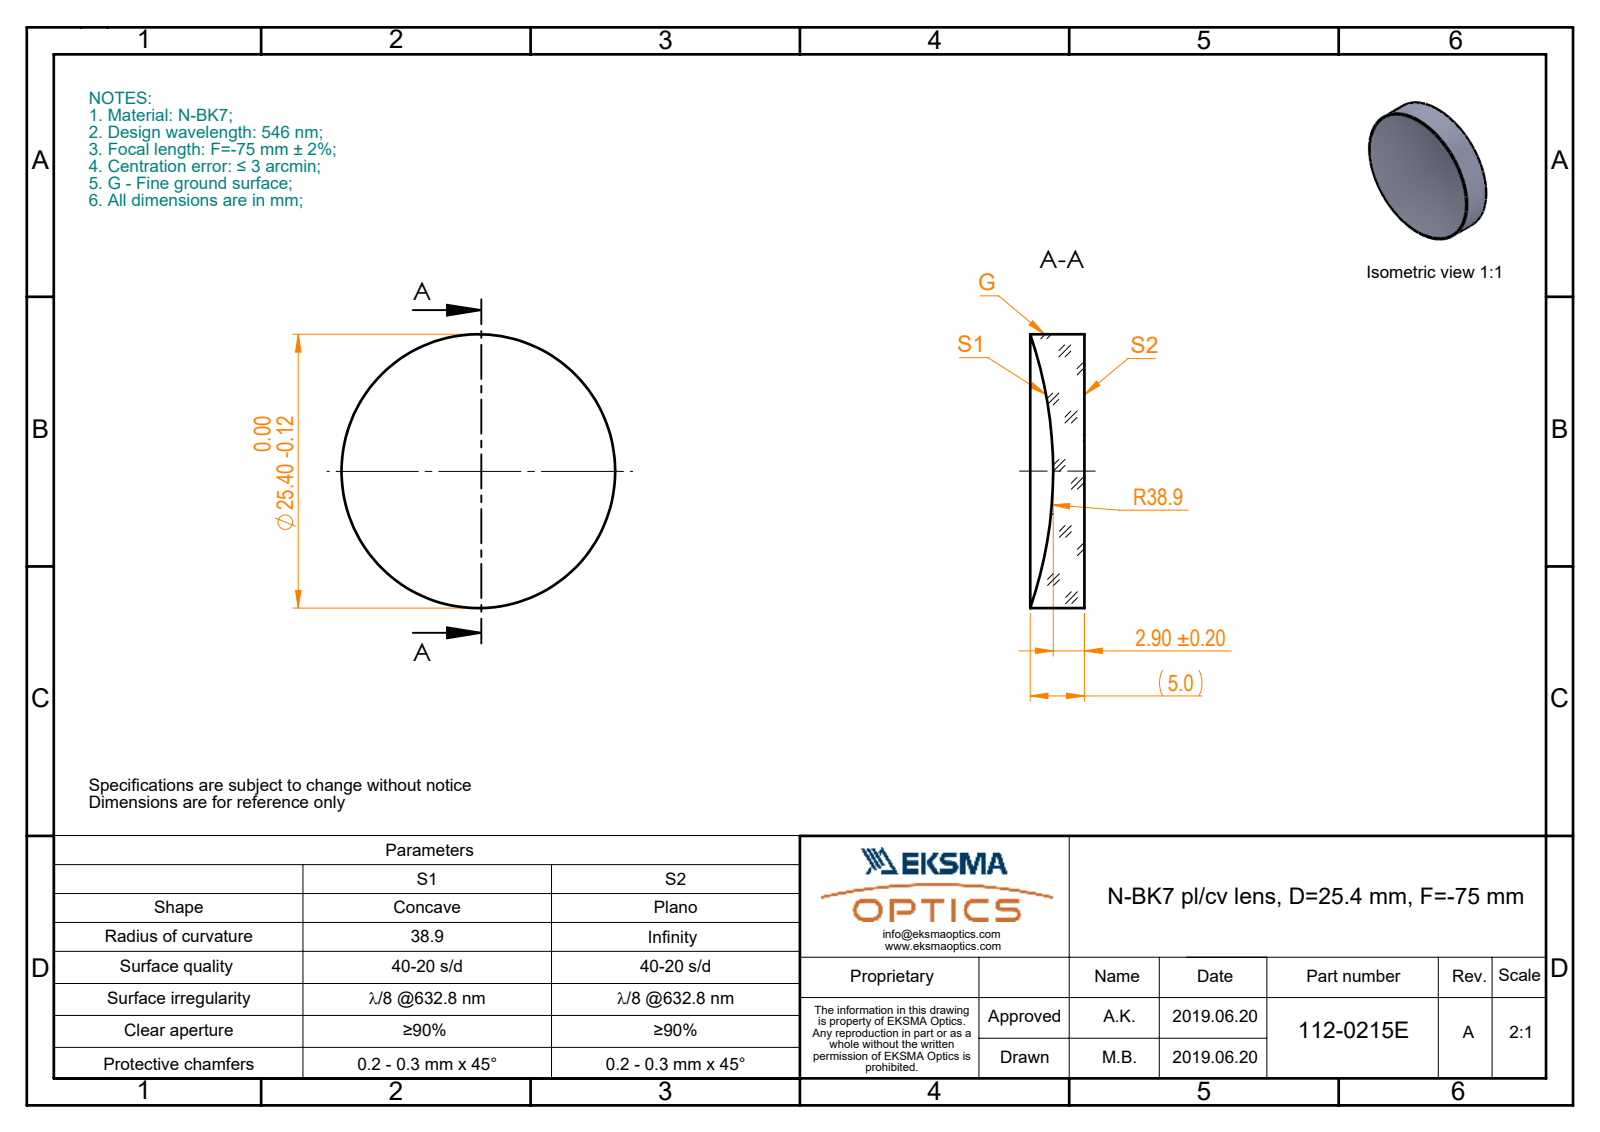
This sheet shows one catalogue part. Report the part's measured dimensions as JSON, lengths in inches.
{"part_name": "112-0215E BK7 pl-cv 25.4 F-75", "step_written_by": "SolidWorks 2017 (CONFIG_CONTROL_DESIGN)", "units": "inches", "bodies": {"solids": 1, "faces": 5, "planar": 1, "cylindrical": 2, "other": 2}, "overall_size": [1, 1, 0.198], "volume_in3": 0.122, "surface_area_in2": 2.215, "round_bosses_or_shafts": [[1, 1]]}
